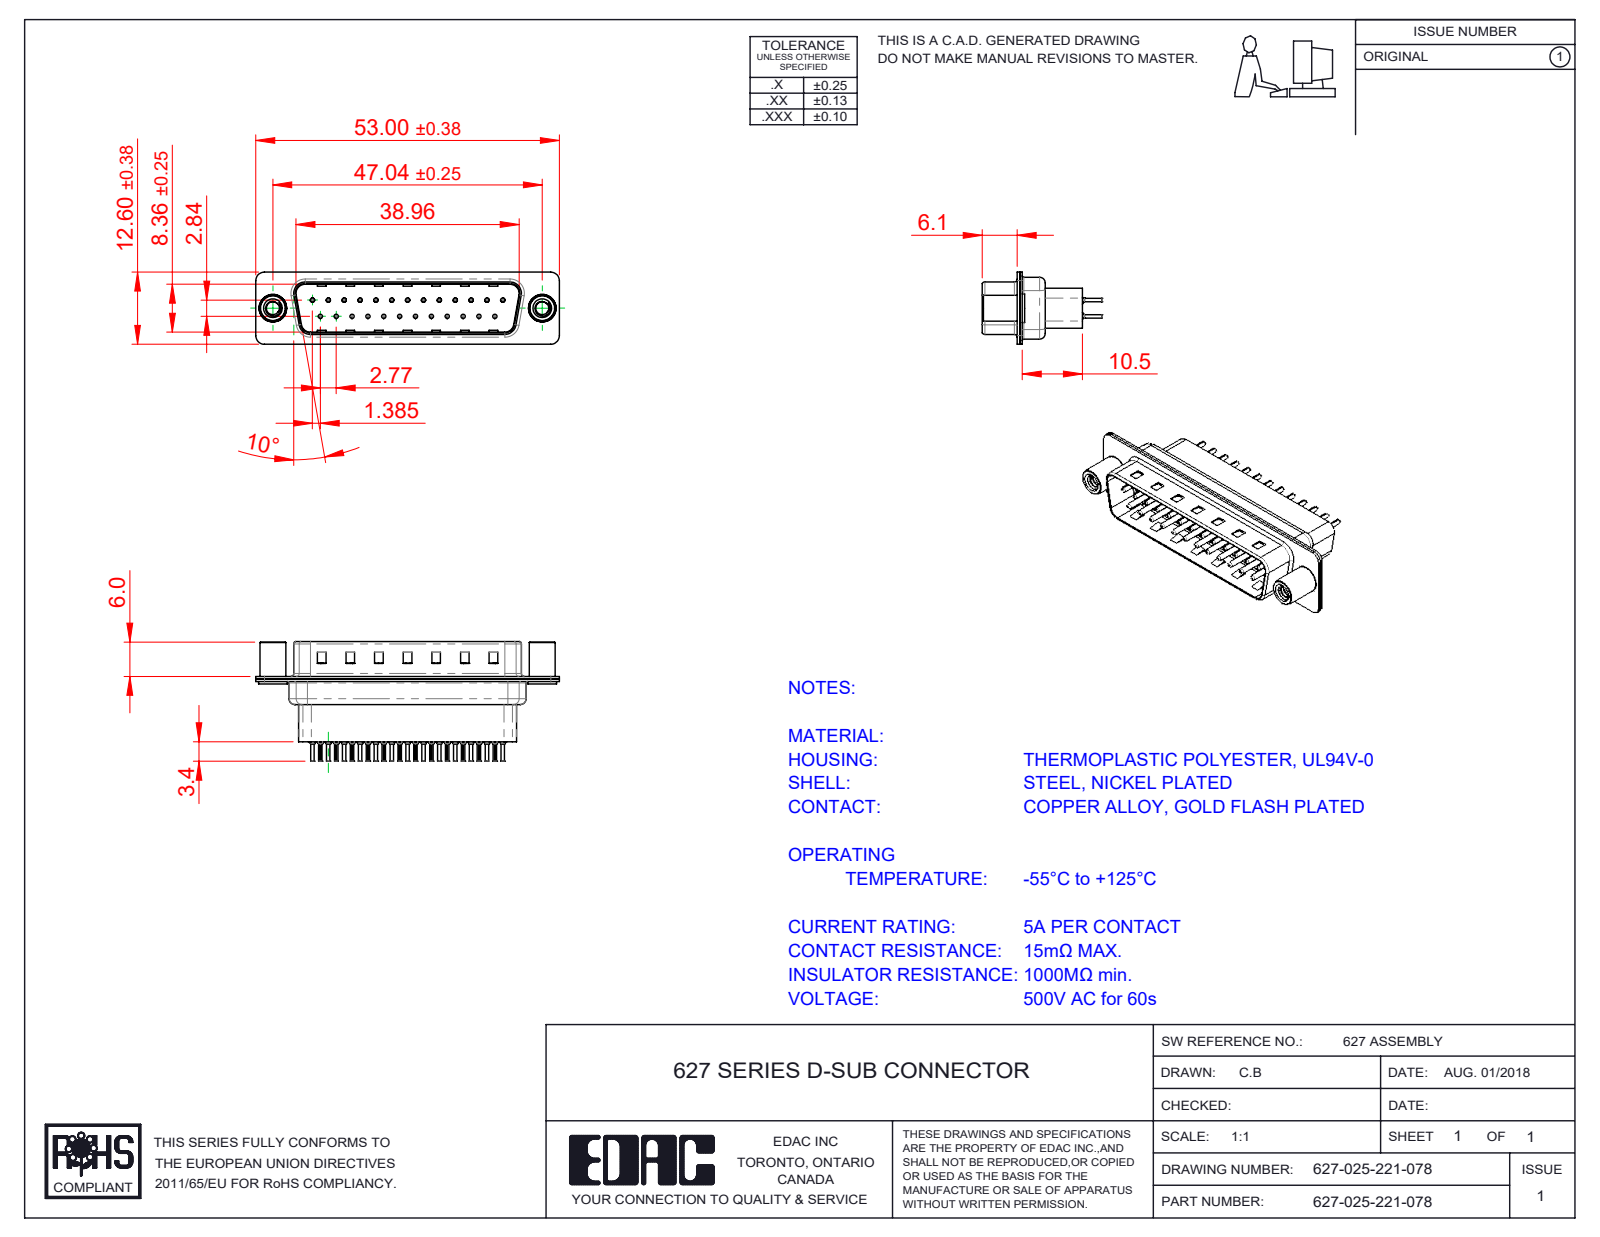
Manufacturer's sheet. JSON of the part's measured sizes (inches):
{"part_name": "627 Shell Rear_25 Contacts; 627 Contact Row 2_21H; 627 Housing_25 HP; 627-025-221-078 (+3 more)", "step_written_by": "SolidWorks 2020 (CONFIG_CONTROL_DESIGN)", "units": "inches", "bodies": {"solids": 30, "faces": 2860, "planar": 773, "cylindrical": 1090, "other": 997}, "overall_size": [2.087, 0.819, 0.496], "volume_in3": 0.236, "surface_area_in2": 15.46, "round_holes": [[0.008, 25], [0.014, 25], [0.043, 25], [0.063, 25], [0.089, 2], [0.157, 2], [0.189, 2]], "round_bosses_or_shafts": [[0.079, 25], [0.059, 25], [0.03, 25], [0.024, 25], [0.197, 2], [0.193, 2], [0.177, 2]], "partial_cylinders_radius": [[0.004, 50], [0.059, 16], [0.079, 12], [0.02, 8], [0.063, 8], [0.01, 4], [0.024, 4], [0.026, 4]], "face_to_face_distances": [0.016, 0.018, 0.032, 0.377, 0.027, 0.302, 0.035, 0.059, 0.043, 0.318], "hole_center_spacings": [0.124, 0.327, 0.109, 0.218, 0.436, 0.654, 0.198, 0.198]}
